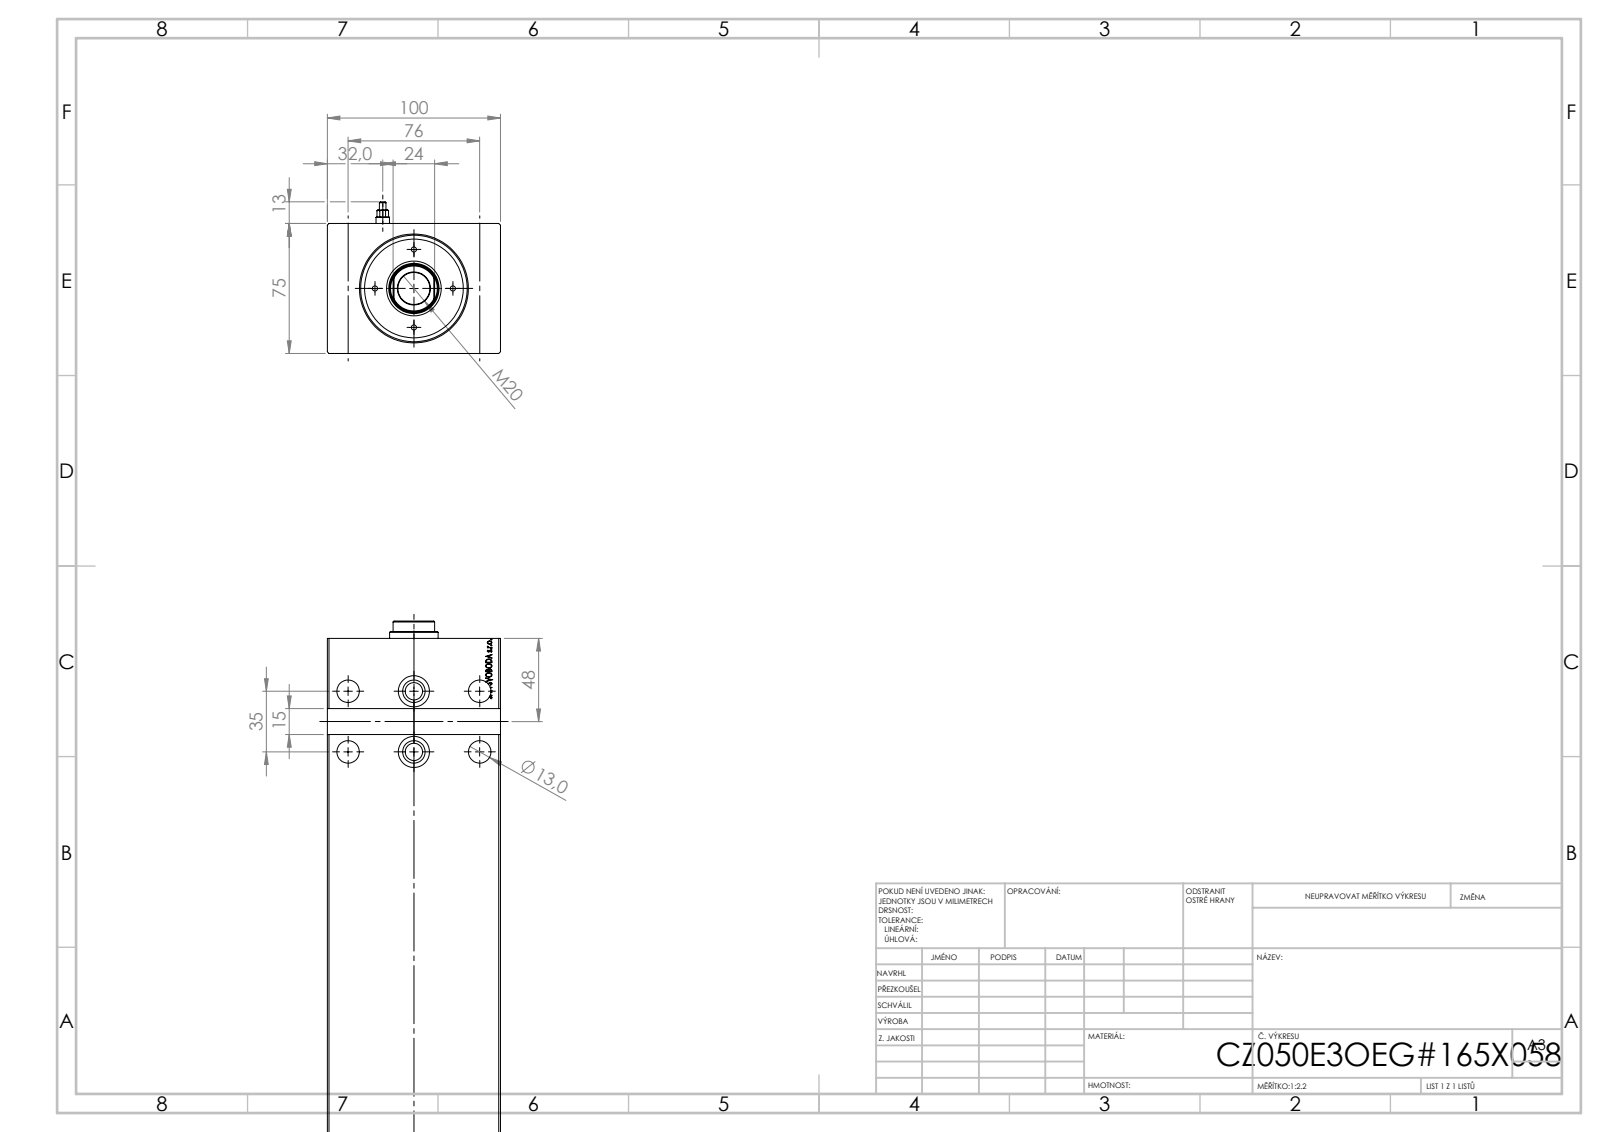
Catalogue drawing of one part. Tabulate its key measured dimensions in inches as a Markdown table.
| quantity | value |
| --- | --- |
| STEP written by | SolidWorks 2019 (CONFIG_CONTROL_DESIGN) |
| units | inches |
| bodies | 1 solid, 775 faces (375 planar, 30 cylindrical, 370 other) |
| overall size | 11.299 × 3.937 × 2.953 |
| volume | 95.75 in³ |
| surface area | 262.9 in² |
| round holes (diameter × count) | 0.512 × 4, 0.315 × 2, 0.394 × 2, 0.709 × 2, 1.417 × 1, 1.969 × 1, 2.421 × 1 |
| round bosses / shafts (diameter × count) | 0.512 × 2 |
| main face-to-face distances | 2.953, 3.937, 11.299, 10.598, 0.701, 0.079, 2.874, 11.291, 0.693, 0.394 |
| hole center spacings | 1.496, 2.034, 1.378, 2.992, 3.294, 0.754, 0.828, 1.327 |
